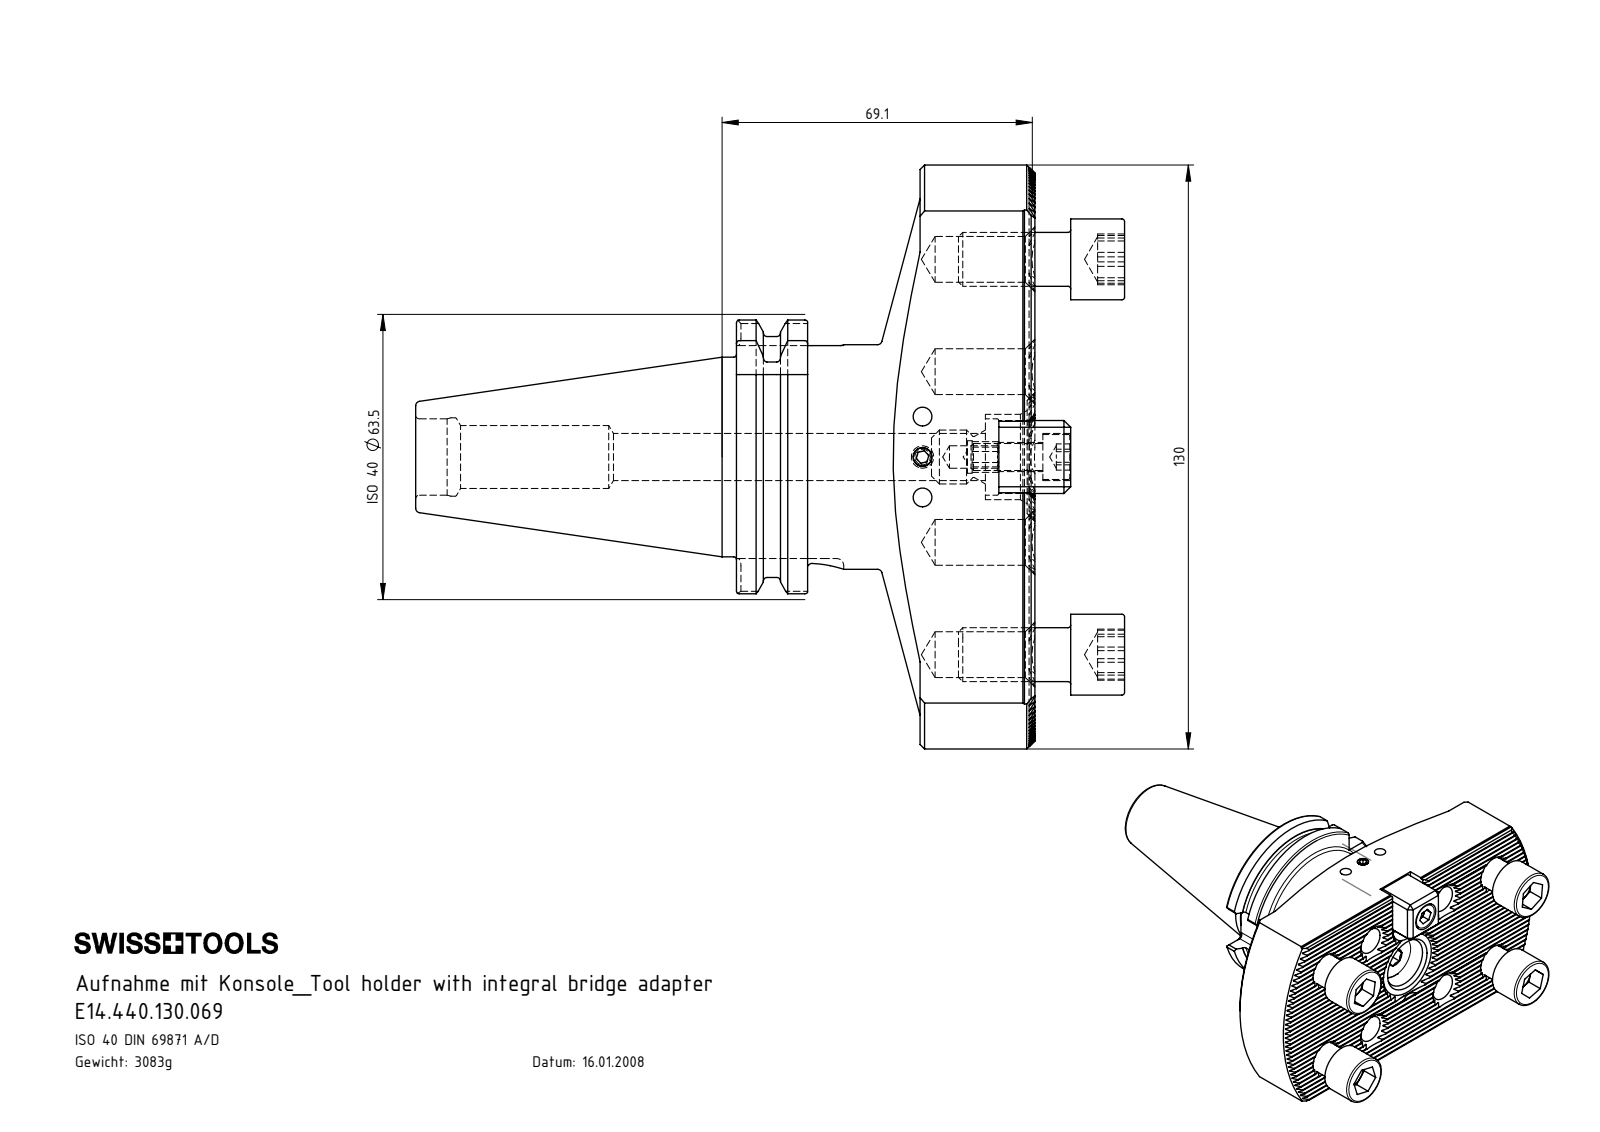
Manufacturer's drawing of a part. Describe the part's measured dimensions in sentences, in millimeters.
The part is named "E14.440.130.069; Ko1-ER1.001.016_A; ISO 4762 M6 x 16; ISO 4762 M12 x 25 (+3 more)". Its 3-D file was written by "SolidWorks 2017 (CONFIG_CONTROL_DESIGN)". It is 10 solids with 886 faces: 502 planar, 210 cylindrical and 174 other. Overall it measures 157.9 by 130 by 70 millimeters. Its volume is 392 696 cubic millimeters and its surface area 72 489 square millimeters. Round holes: 8 of diameter 10.2, 3 of diameter 4.2, 2 of diameter 10.5, 1 of diameter 5, 1 of diameter 6.5, 1 of diameter 7.24, 1 of diameter 14, 1 of diameter 17, 1 of diameter 17.45, 1 of diameter 19. Round bosses or shafts: 5 of diameter 12, 4 of diameter 18, 1 of diameter 50, 1 of diameter 44.45, 1 of diameter 10, 1 of diameter 6, 1 of diameter 5. Partial cylindrical surfaces (rounded edges, fillets, slot ends): 34 of radius 0.14, 8 of radius 1.6, 1 of radius 7.95, 1 of radius 8, 1 of radius 8.05, 1 of radius 28, 1 of radius 31.75, 1 of radius 65. The main face-to-face distances are 1.73, 17.32, 70, 8.66, 3.46, 5.2, 6.93, 15.59, 19.05, 3.47. The hole center spacings are 25, 27.59, 40, 47.17, 48.33, 63, 74.63, 9.
